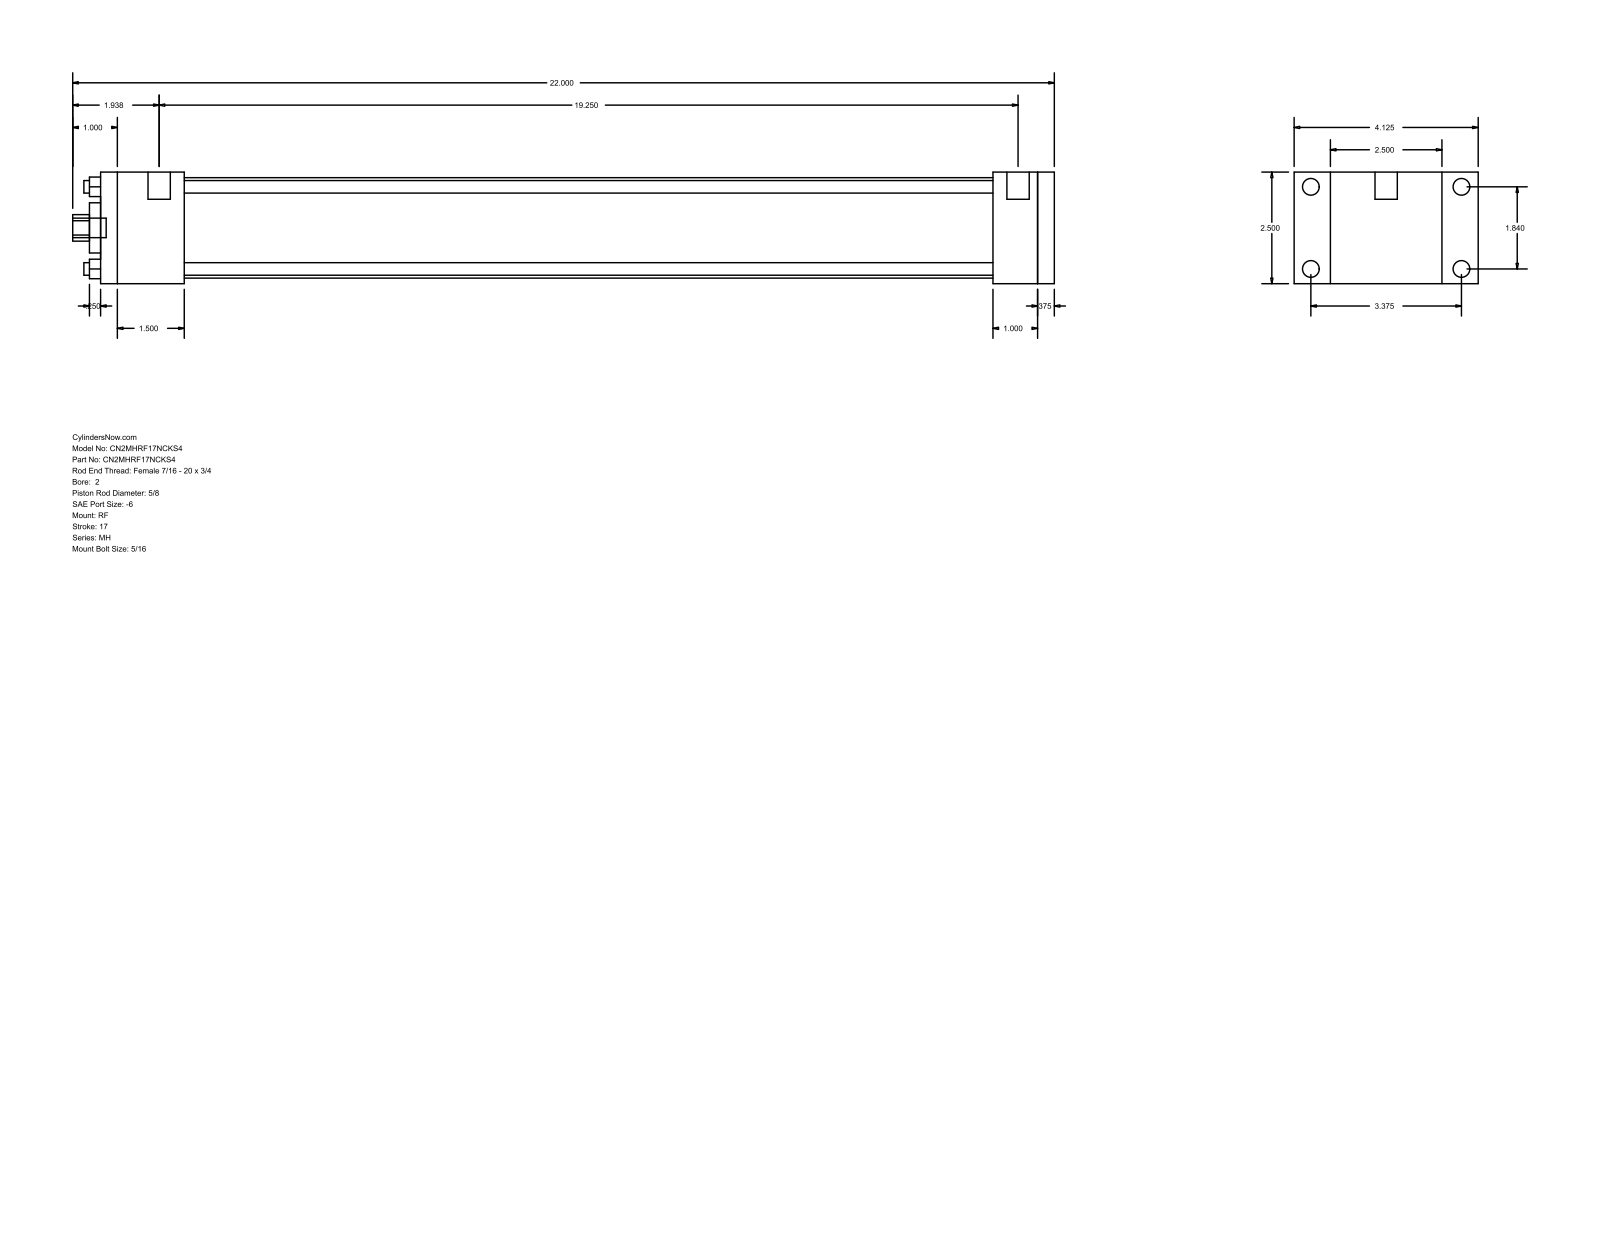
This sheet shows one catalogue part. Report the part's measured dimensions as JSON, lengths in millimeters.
{"part_name": "MH_RF__0200_0.625", "step_written_by": "GSSL Pune (CONFIG_CONTROL_DESIGN)", "units": "millimeters", "bodies": {"solids": 0, "faces": 92, "planar": 64, "cylindrical": 28, "other": 0}, "overall_size": [558.8, 104.78, 63.5], "round_holes": [[7.14, 4], [15.88, 1], [28.57, 1], [57.15, 1]], "round_bosses_or_shafts": [[9.53, 4], [5.56, 4], [12.7, 2], [11.11, 1]], "partial_cylinders_radius": [[7.54, 1]], "face_to_face_distances": [63.5, 542.92, 9.53, 533.39, 47.62, 508, 460.38, 485.77, 495.3, 25.39], "hole_center_spacings": [33.05, 46.74, 66.1]}
